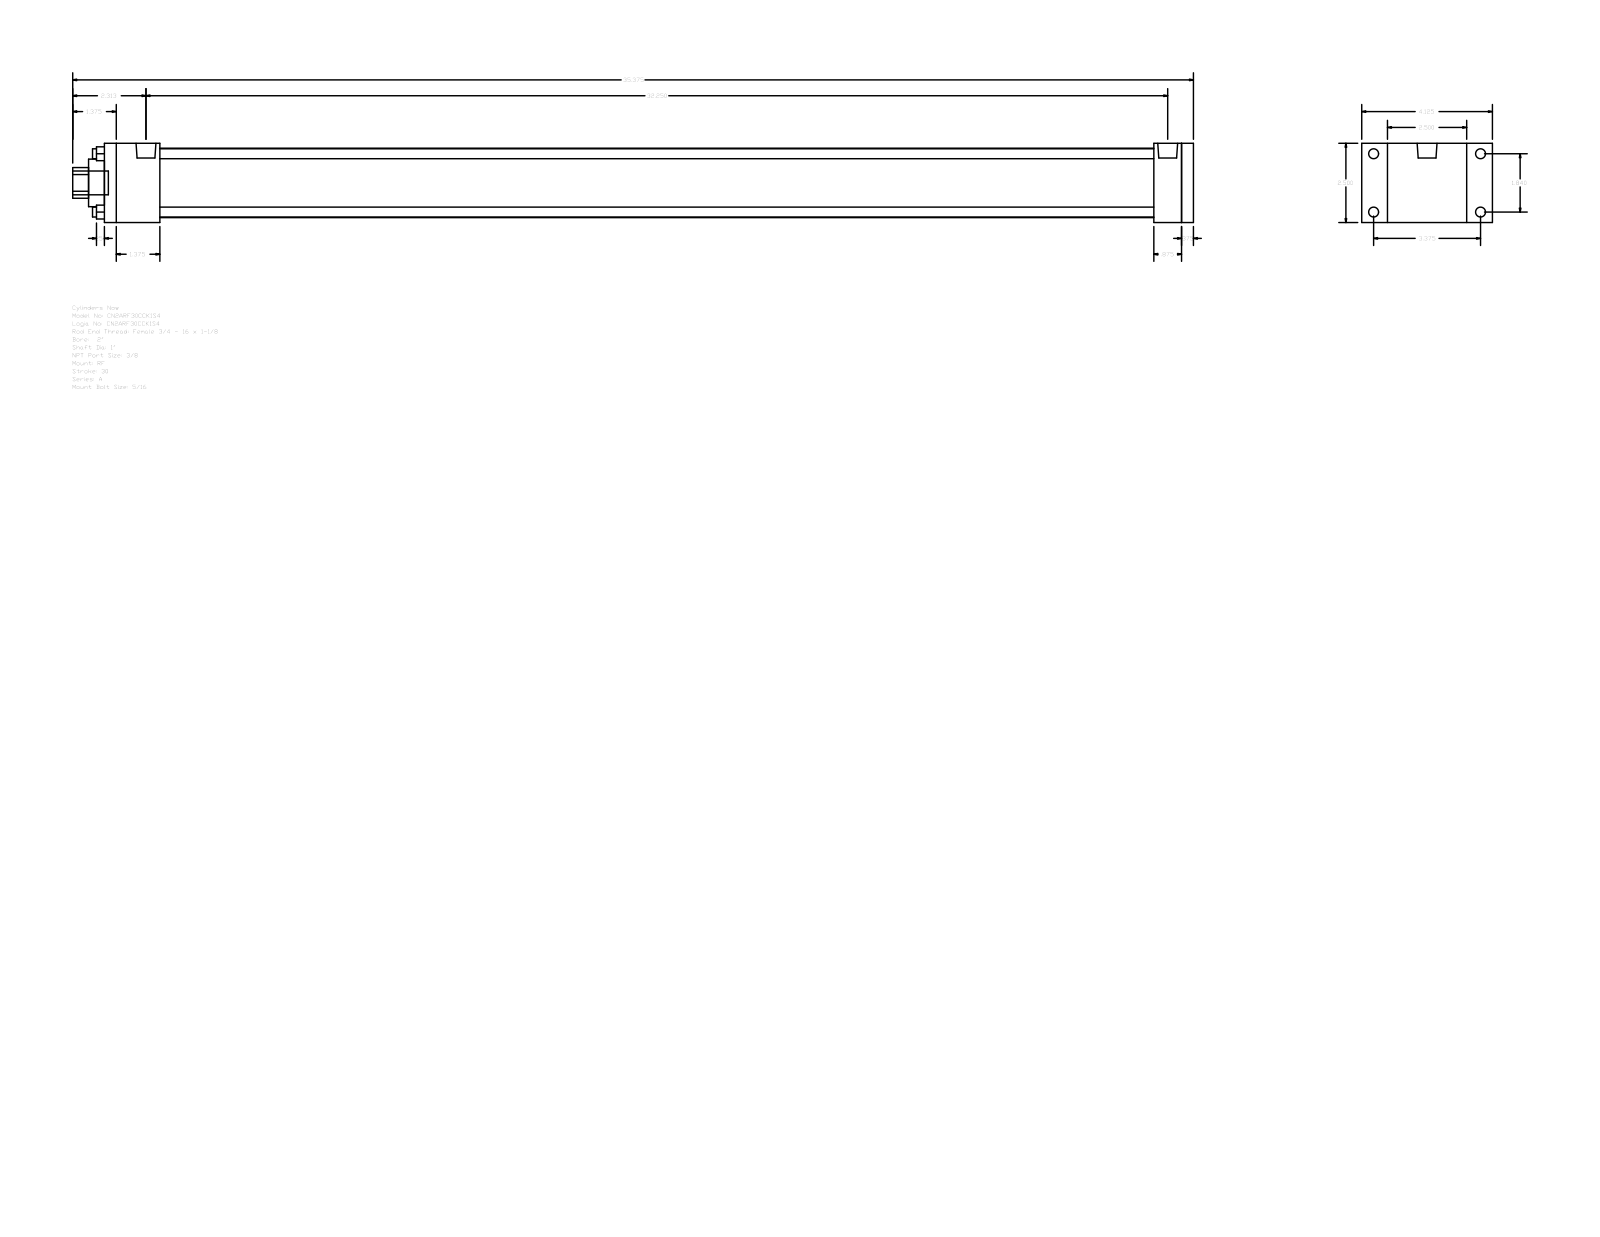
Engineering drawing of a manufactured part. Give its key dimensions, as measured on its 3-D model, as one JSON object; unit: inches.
{"part_name": "A_RF__0200_1", "step_written_by": "GSSL Pune (CONFIG_CONTROL_DESIGN)", "units": "inches", "bodies": {"solids": 0, "faces": 92, "planar": 64, "cylindrical": 28, "other": 0}, "overall_size": [35.375, 4.125, 2.5], "round_holes": [[0.313, 4], [1, 1], [1.5, 1], [2.19, 1]], "round_bosses_or_shafts": [[0.313, 4], [0.219, 4], [0.627, 2], [0.75, 1]], "partial_cylinders_radius": [[0.484, 1]], "face_to_face_distances": [2.5, 0.375, 34.375, 34, 0.813, 1.75, 32.25, 32.625, 33.125, 31.375], "hole_center_spacings": [1.301, 1.84, 2.602]}
